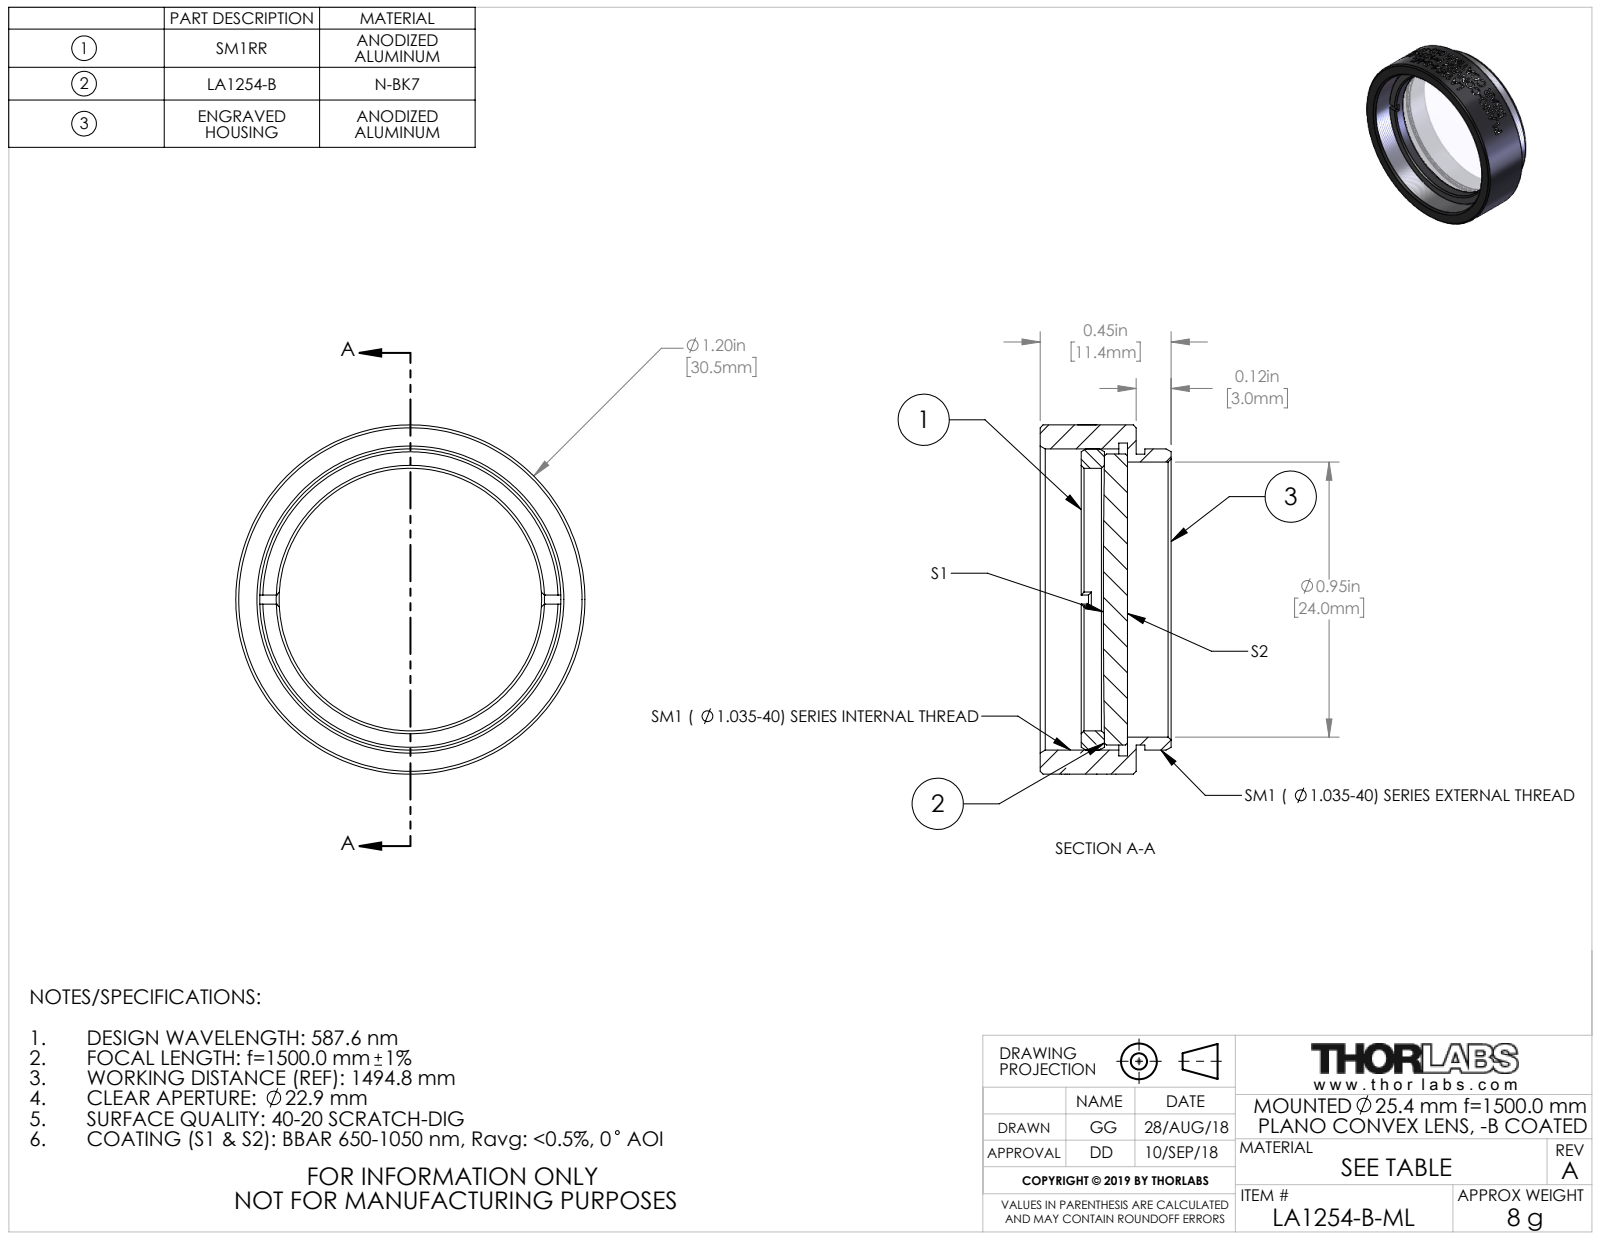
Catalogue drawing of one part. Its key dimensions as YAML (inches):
part_name: "TTN162136-E0W"
step_written_by: "SolidWorks 2018 (CONFIG_CONTROL_DESIGN)"
units: inches
bodies: {solids: 3, faces: 181, planar: 20, cylindrical: 133, other: 28}
overall_size: [1.2, 1.2, 0.45]
volume: 0.19
surface_area: 6.659
round_holes:
  - {diameter: 0.902, count: 1}
  - {diameter: 0.945, count: 1}
  - {diameter: 1.075, count: 1}
round_bosses_or_shafts:
  - {diameter: 1.2, count: 1}
  - {diameter: 1.035, count: 1}
  - {diameter: 1, count: 1}
  - {diameter: 0.999, count: 1}
face_to_face_distances: [0.03, 0.33, 0.3, 0.109, 0.079, 0.221, 0.189, 0.159, 0.08, 0.141]
